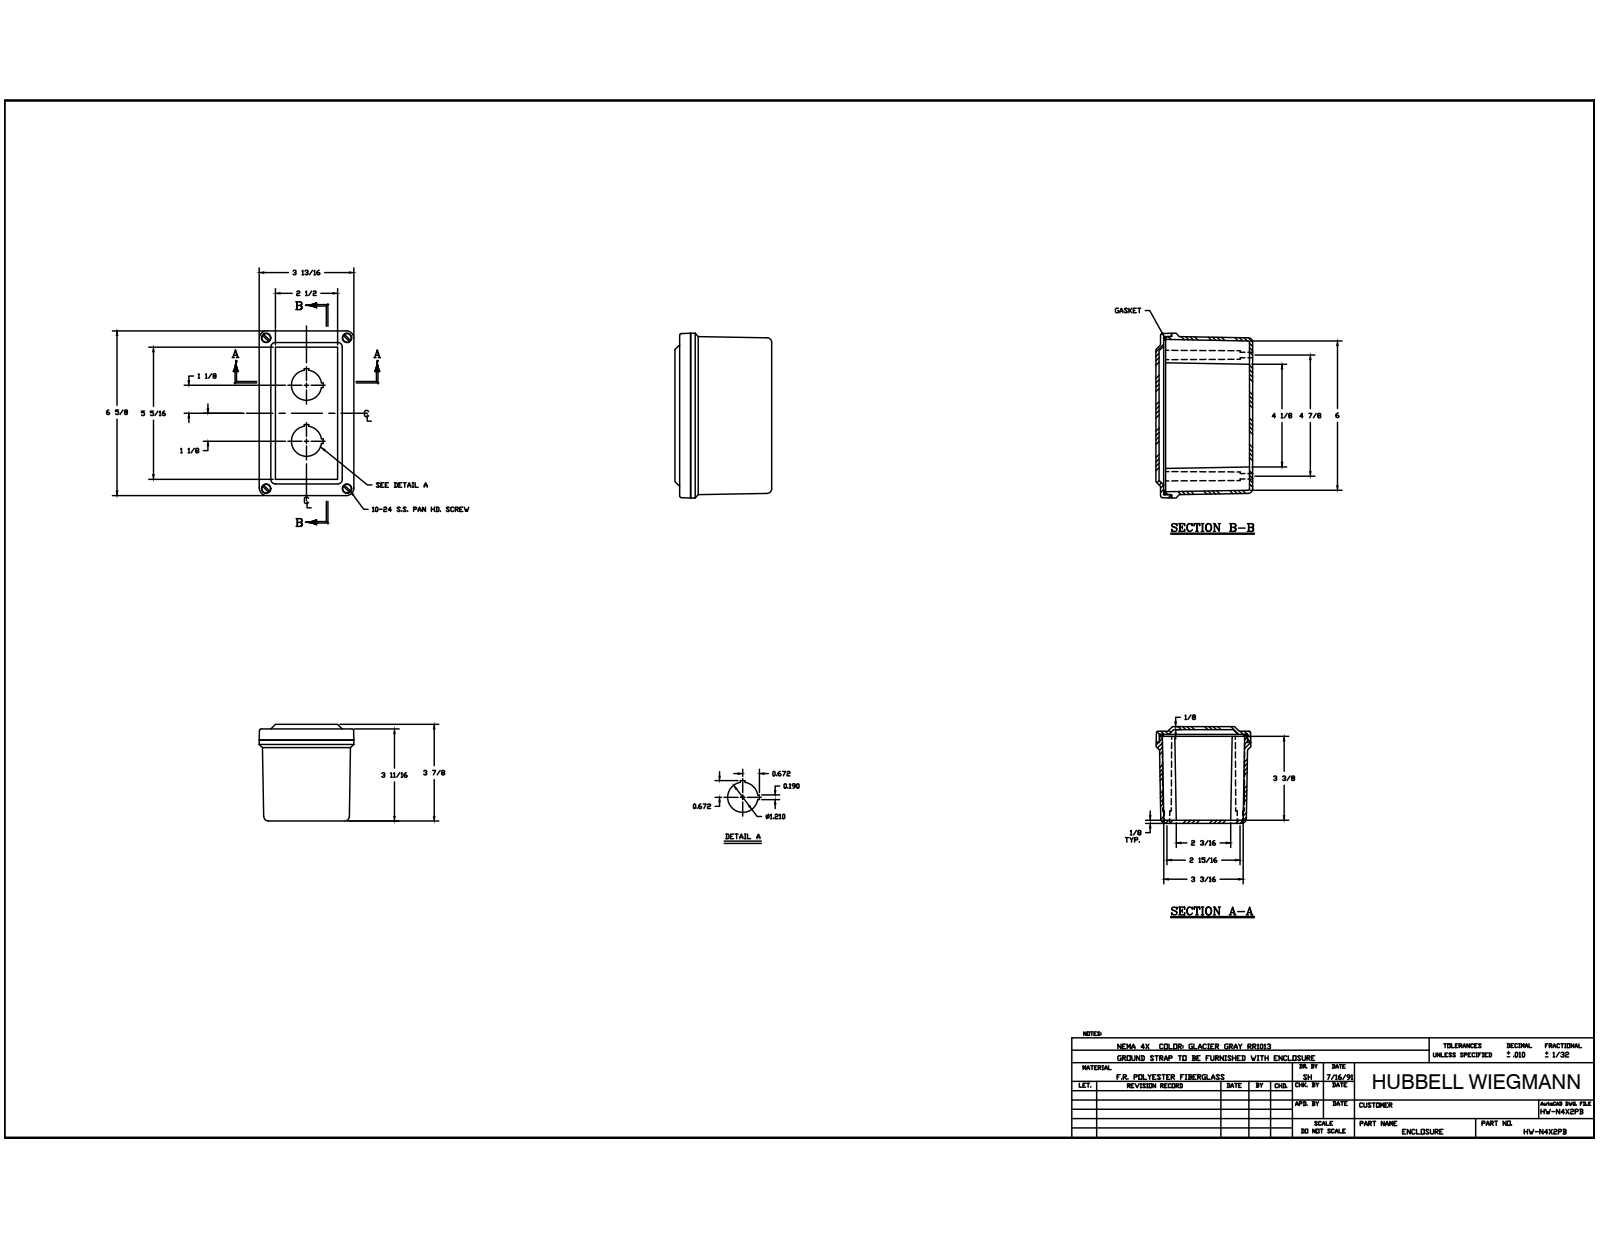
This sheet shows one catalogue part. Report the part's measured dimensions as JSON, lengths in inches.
{"part_name": "WPCF644 BOX; 10-24 X 0.4375 DP BRASS INSERT; WPCF2PB CVR; WPCF644 GASKET (+3 more)", "step_written_by": "Autodesk Inventor 2014 (AUTOMOTIVE_DESIGN)", "units": "inches", "bodies": {"solids": 11, "faces": 395, "planar": 195, "cylindrical": 108, "other": 92}, "overall_size": [6.625, 3.875, 3.813], "volume_in3": 20.22, "surface_area_in2": 264, "round_holes": [[0.219, 8], [0.145, 4], [0.19, 4], [0.375, 4], [1.21, 2]], "round_bosses_or_shafts": [[0.371, 4], [0.218, 4], [0.177, 4]], "partial_cylinders_radius": [[0.031, 20], [0.012, 16], [0.313, 8], [0.063, 4], [0.176, 4], [0.187, 4], [0.22, 4], [0.325, 4]], "face_to_face_distances": [0.125, 0.135, 3.75, 0.187, 3.563, 0.5, 3.875, 0.063, 3.625, 3.438], "hole_center_spacings": [0.614, 3.15, 5.471, 6.283, 1.97, 1.97, 2.504, 2.505]}
